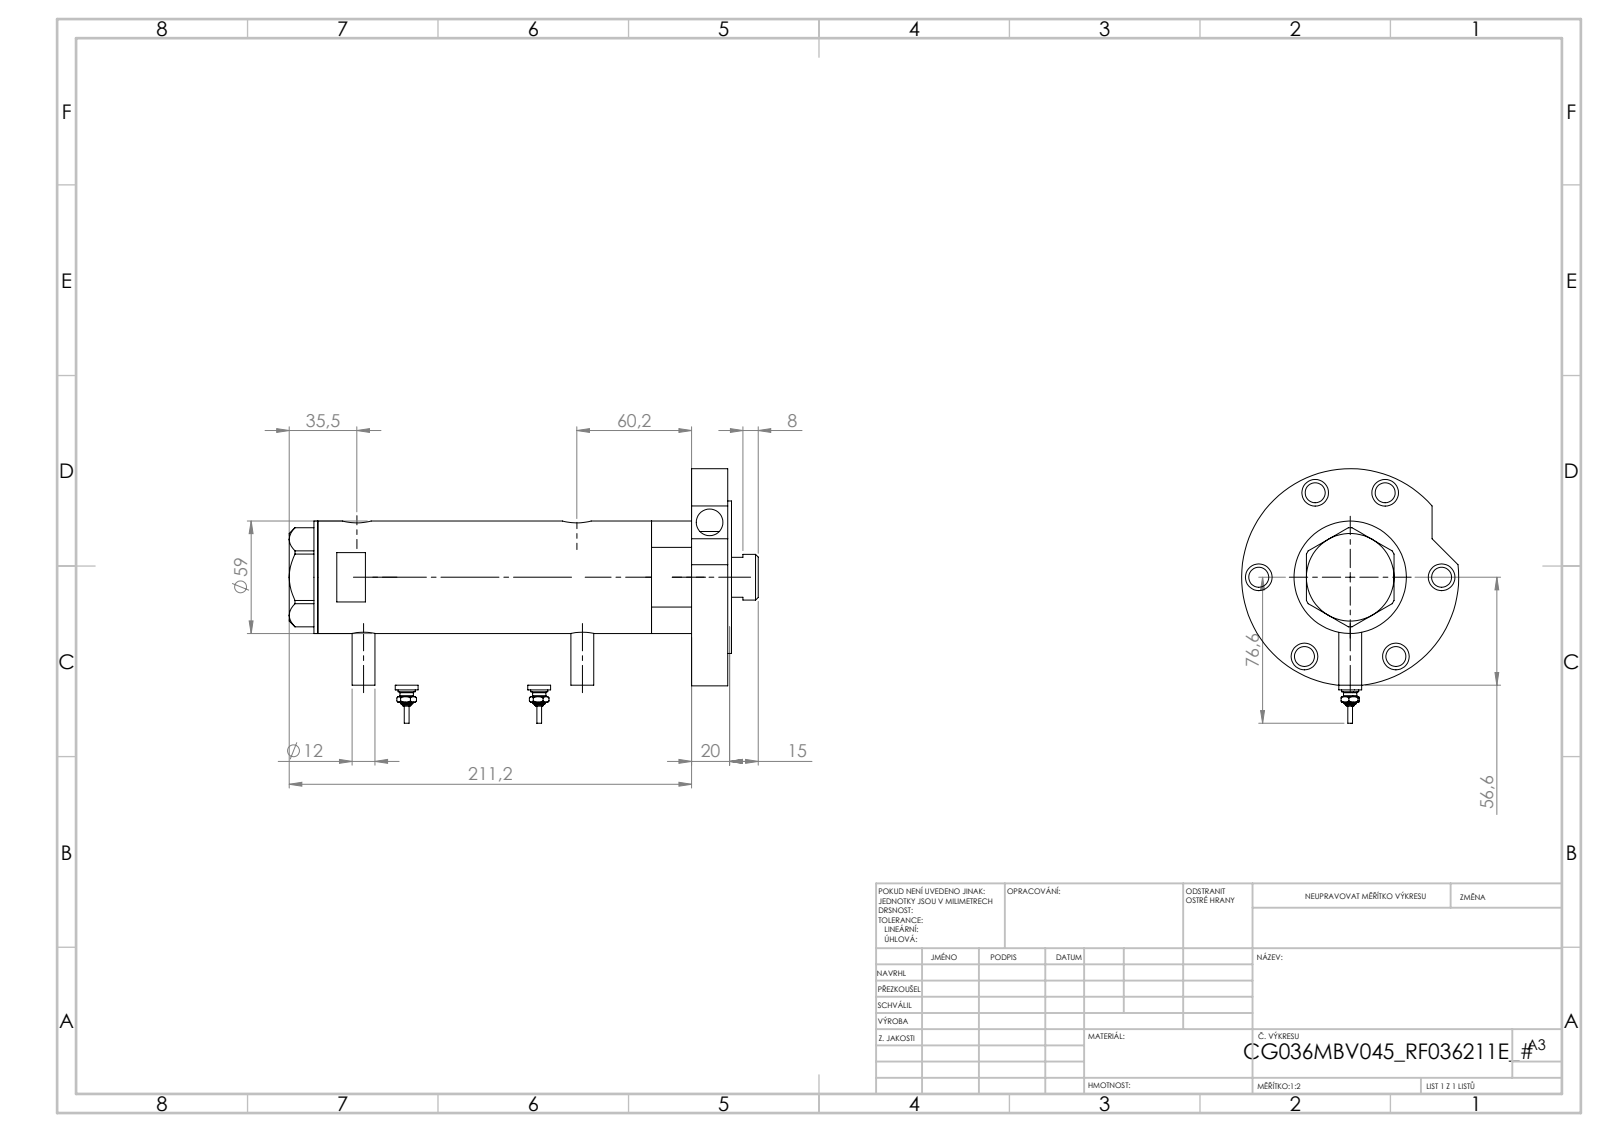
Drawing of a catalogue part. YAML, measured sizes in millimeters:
part_name: "V270CG_BACK; V270CG_MIDDLE; V270CG_VC; Switch (+2 more)"
step_written_by: "SolidWorks 2019 (CONFIG_CONTROL_DESIGN)"
units: millimeters
bodies: {solids: 7, faces: 256, planar: 90, cylindrical: 102, other: 64}
overall_size: [246.2, 133.6, 114]
volume: 718964
surface_area: 150802
round_holes:
  - {diameter: 14, count: 7}
  - {diameter: 10.5, count: 6}
  - {diameter: 9.73, count: 2}
  - {diameter: 12.5, count: 2}
  - {diameter: 15, count: 2}
  - {diameter: 8.5, count: 1}
  - {diameter: 25, count: 1}
  - {diameter: 26.5, count: 1}
  - {diameter: 36, count: 1}
  - {diameter: 40, count: 1}
  - {diameter: 48, count: 1}
  - {diameter: 52, count: 1}
round_bosses_or_shafts:
  - {diameter: 12, count: 4}
  - {diameter: 9, count: 2}
  - {diameter: 7, count: 2}
  - {diameter: 4.5, count: 2}
  - {diameter: 2.5, count: 2}
  - {diameter: 114, count: 1}
  - {diameter: 80, count: 1}
  - {diameter: 59, count: 1}
face_to_face_distances: [2, 19, 21, 217.2, 196.2, 215.2, 137.2, 59, 78, 80]
hole_center_spacings: [48, 53.34, 79.82, 83.14, 86.1, 95.8, 2.9, 3.5]
